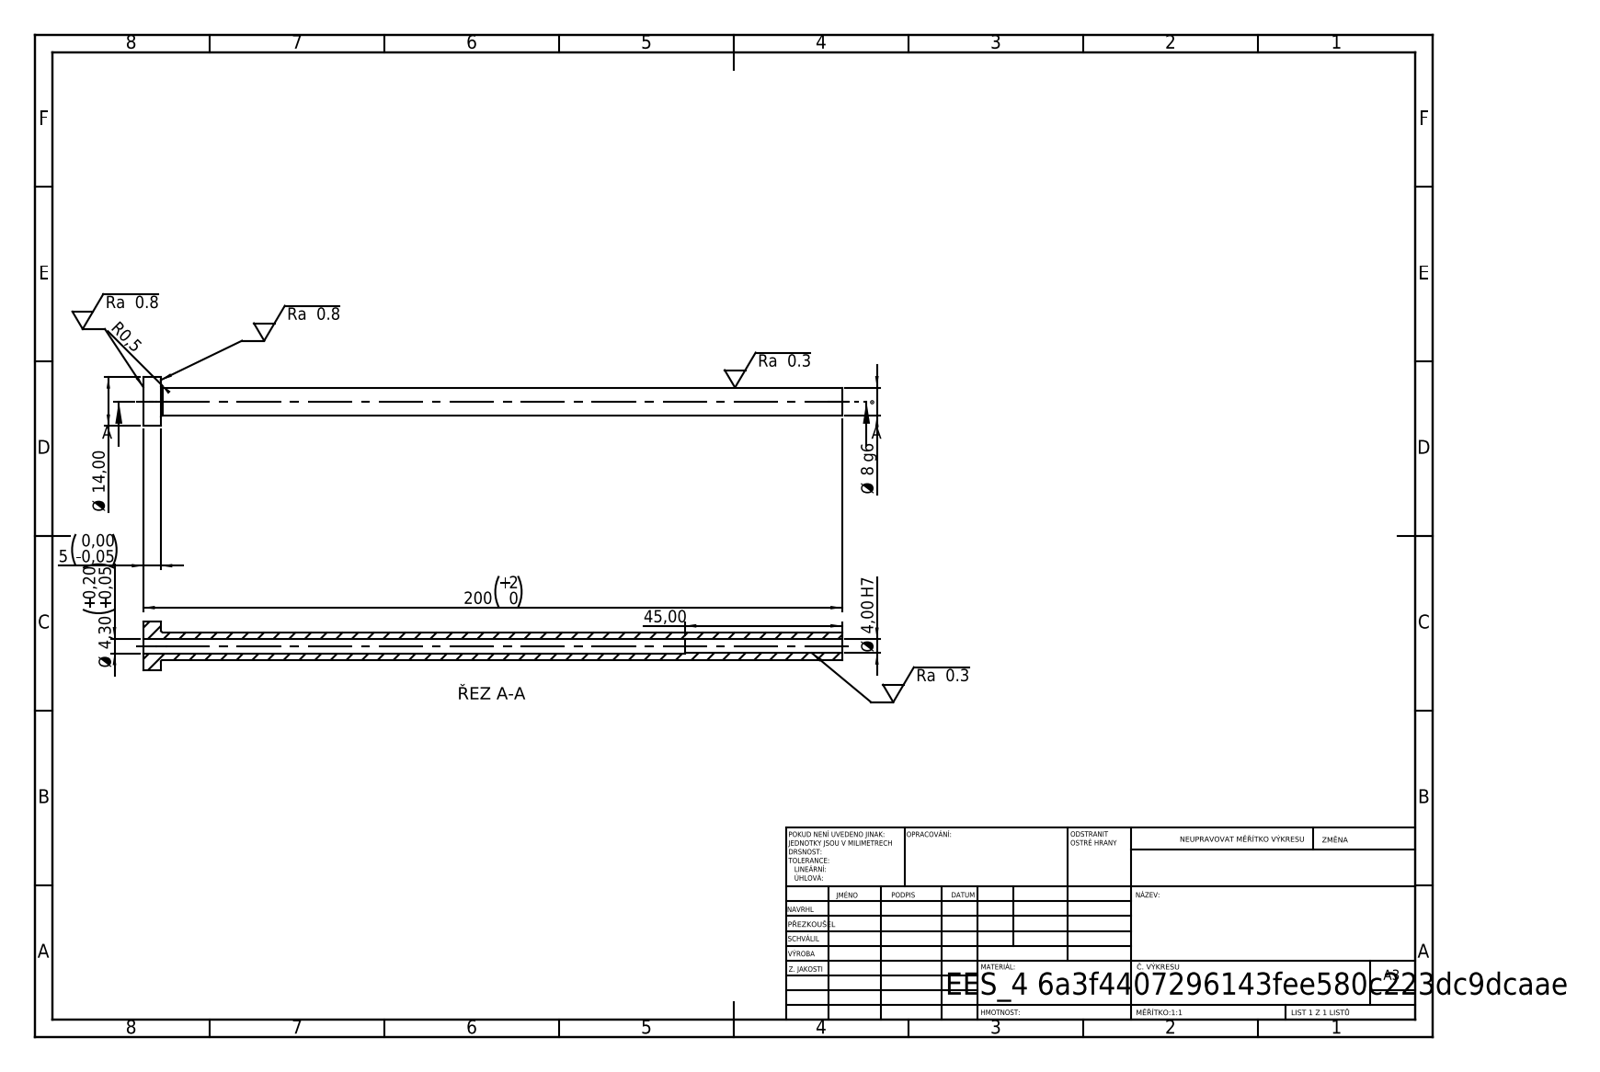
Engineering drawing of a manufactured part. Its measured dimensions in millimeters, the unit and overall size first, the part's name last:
Units: millimetres
Overall size (bounding box): 200 × 14 × 14
Round holes (diameter × count): ⌀4 ×1, ⌀4.3 ×1
Round bosses / shafts (diameter × count): ⌀14 ×1, ⌀8 ×1
Main face-to-face distances: 5, 200, 195, 155, 150, 45
Volume: 7 756 mm³ · Surface area: 8 058 mm²
Bodies: 1 solid, 14 faces (4 planar, 8 cylindrical, 2 other)
STEP written by: SolidWorks 2019 (CONFIG_CONTROL_DESIGN)
